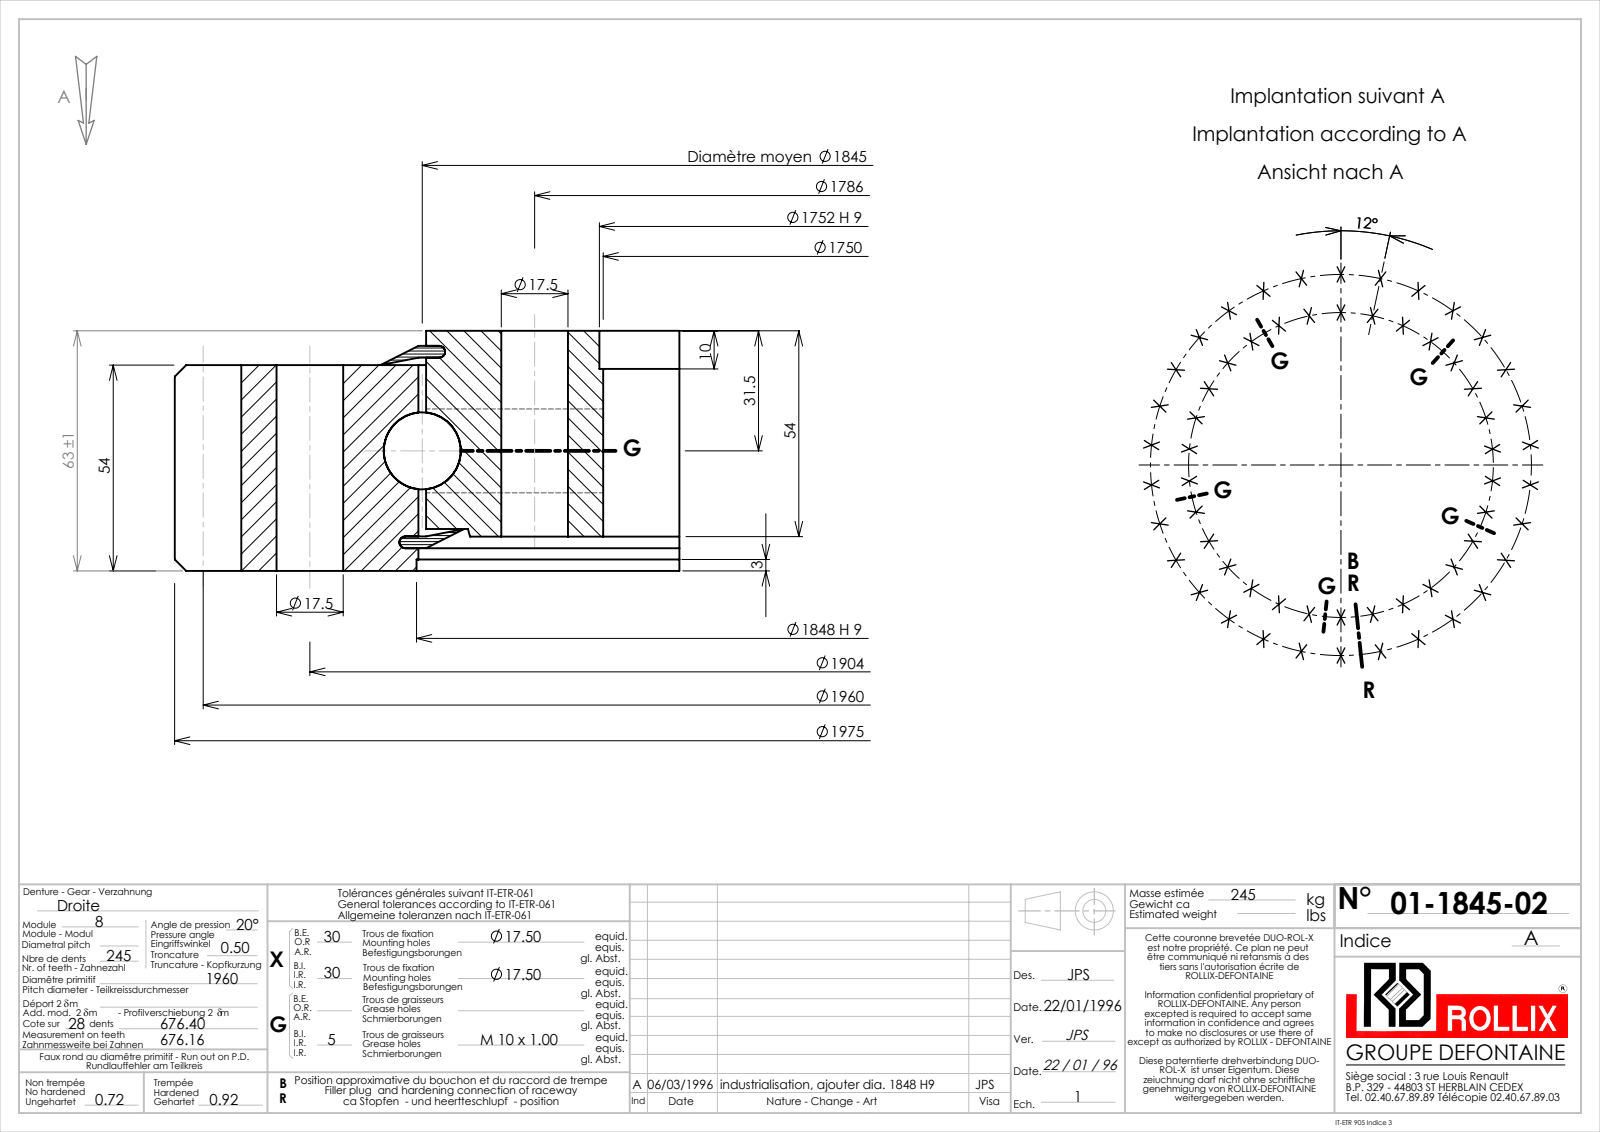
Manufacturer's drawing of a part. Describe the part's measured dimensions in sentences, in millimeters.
The part is named "01-1845-02". Its 3-D file was written by "SolidWorks 2016 (CONFIG_CONTROL_DESIGN)". It is 5 solids with 1665 faces: 505 planar, 639 cylindrical and 521 other. Overall it measures 1974.99 by 1974.96 by 63 millimeters. Its volume is 29 840 000 cubic millimeters and its surface area 3 560 000 square millimeters. Round holes: 60 of diameter 17.5, 5 of diameter 9, 1 of diameter 1750, 1 of diameter 1752, 1 of diameter 1847.02, 1 of diameter 1848. Round bosses or shafts: 1 of diameter 1842.98. Partial cylindrical surfaces (rounded edges, fillets, slot ends): 1 of radius 970, 1 of radius 987.5. The main face-to-face distances are 54, 9, 63, 45, 50, 5.05, 48.05, 1.95, 44.95, 3.1. The hole center spacings are 1648.91, 1862.39, 199.02, 774.42, 952, 588.37, 1540.37, 395.86.
